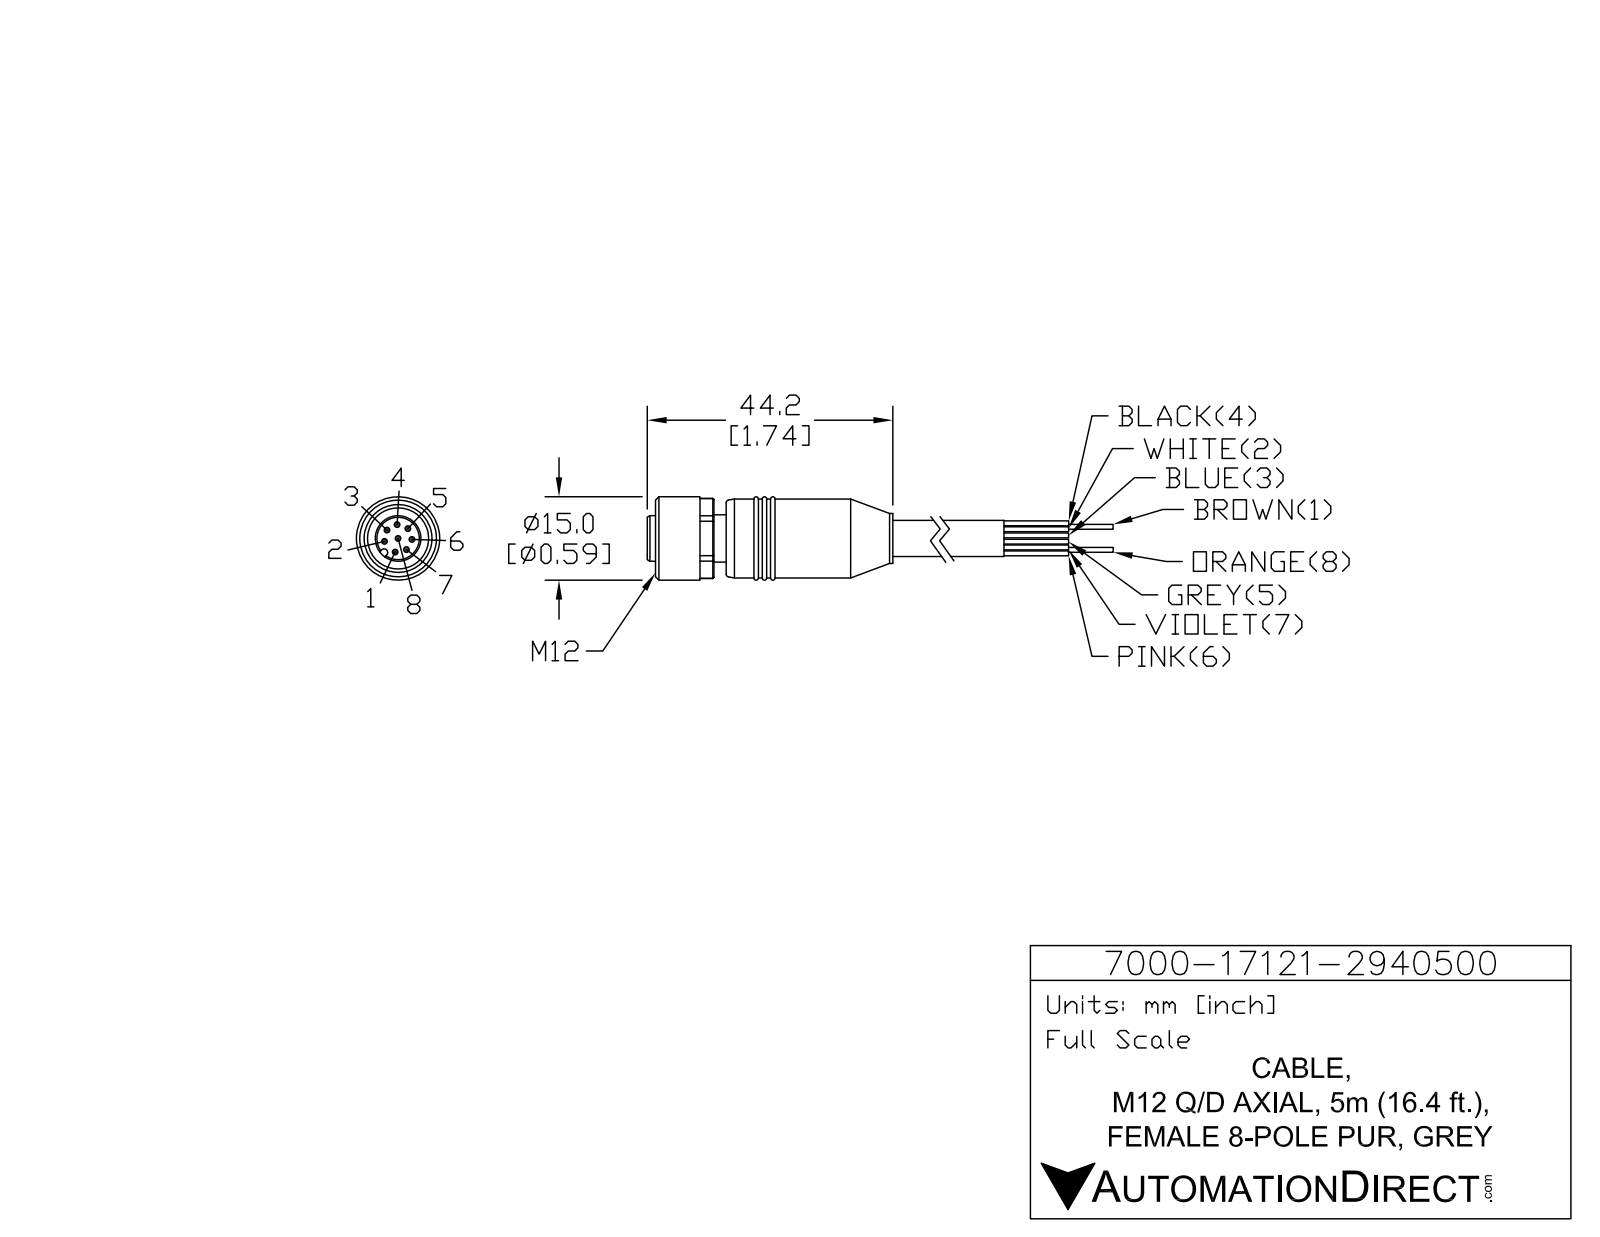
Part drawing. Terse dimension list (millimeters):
name: 7000-17121-2940500
written by: SolidWorks 2015 (AUTOMOTIVE_DESIGN)
unit: mm
bodies: 1 solid, 103 faces (31 planar, 44 cylindrical, 28 other)
size: 64.2 × 15 × 15
volume: 6 618 mm³; area: 3 393 mm²
holes: 8× ⌀1, 1× ⌀11
bosses: 1× ⌀15, 1× ⌀14.2, 1× ⌀9, 1× ⌀8.5, 1× ⌀8.2, 1× ⌀6.5
rounds: 1× R0.65, 1× R7.2
face distances: 2.2, 13, 3, 5.2, 9, 12, 14.2, 64.2, 55.2, 52.2
hole spacings: 2.5, 2.07, 3.78, 4.95, 2.08, 4.22, 4.79, 4.8
